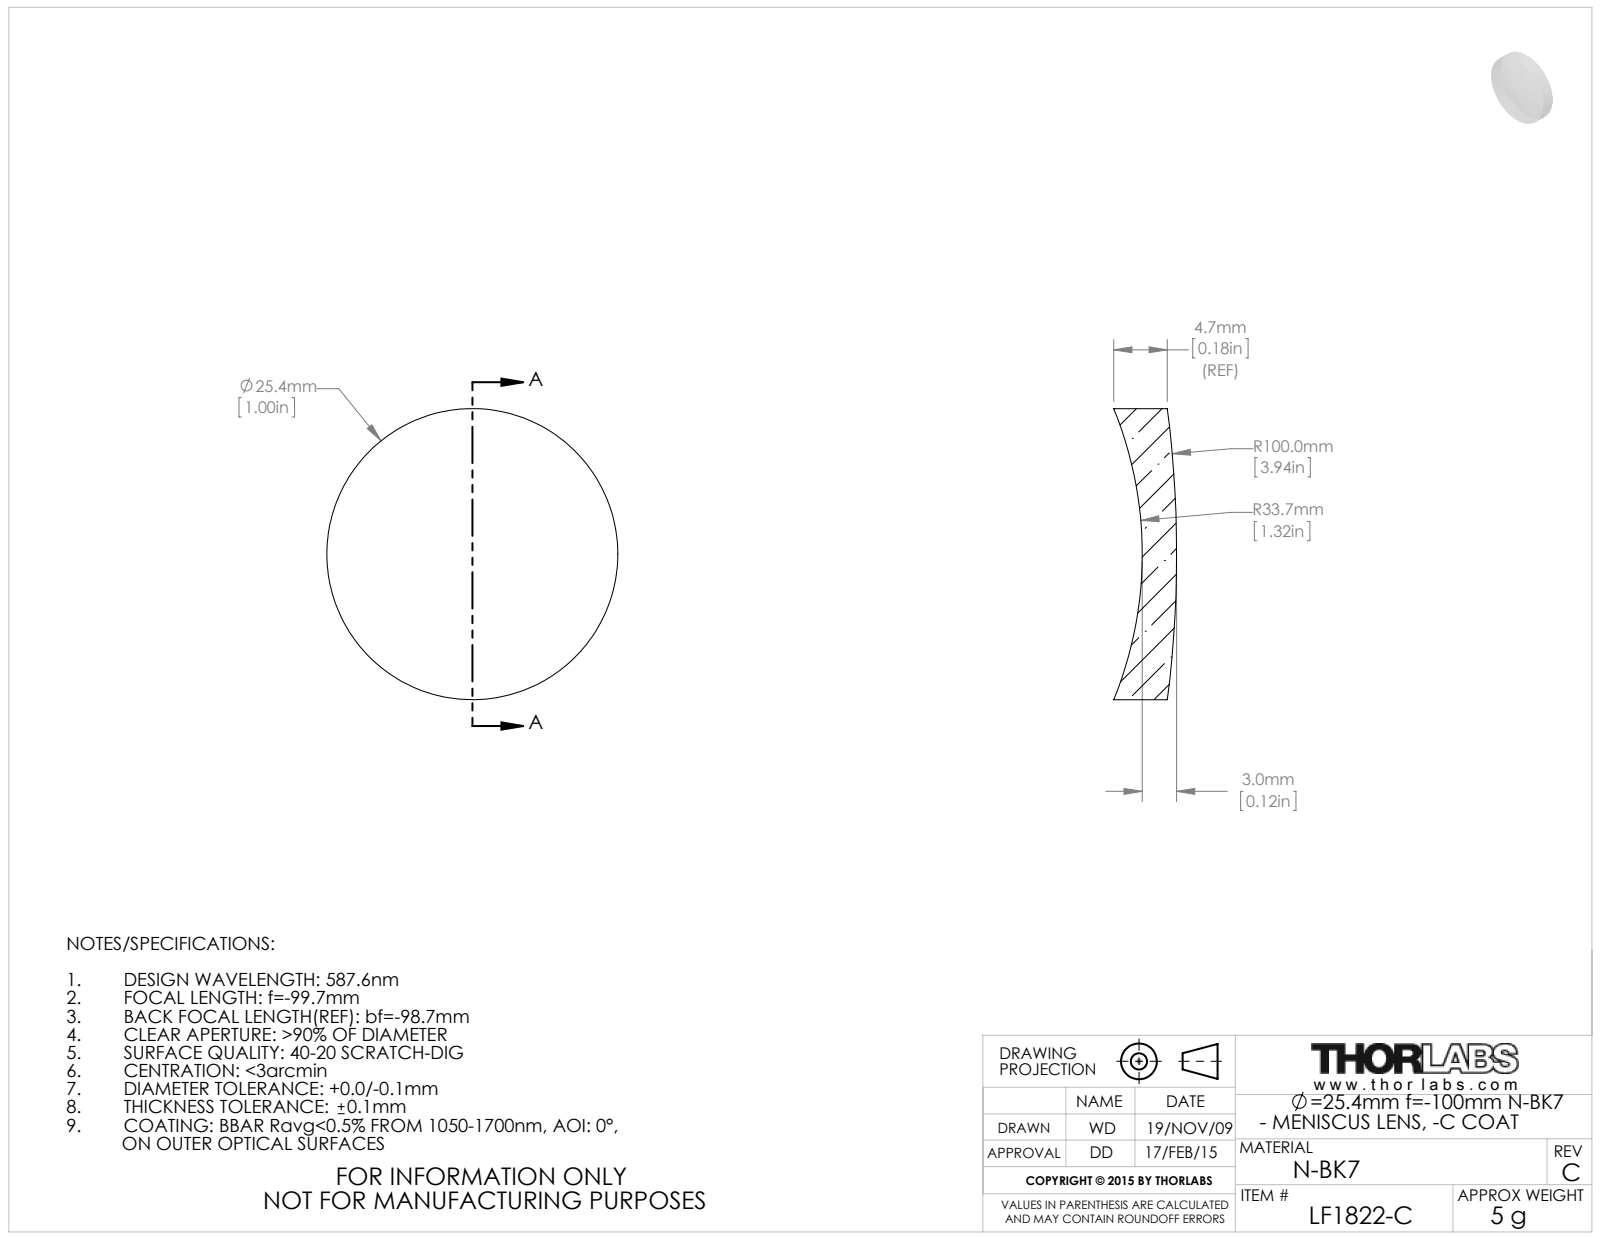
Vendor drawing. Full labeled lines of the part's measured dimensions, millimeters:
Part name (STEP PRODUCT): 4905-E0W
STEP written by: SolidWorks 2009 (AUTOMOTIVE_DESIGN)
Units: millimetres
Bodies: 1 solid, 6 faces (0 planar, 2 cylindrical, 4 other)
Overall size (bounding box): 25.4 × 25.4 × 5.49
Volume: 1 938 mm³ · Surface area: 1 408 mm²
Round bosses / shafts (diameter × count): ⌀25.4 ×1
